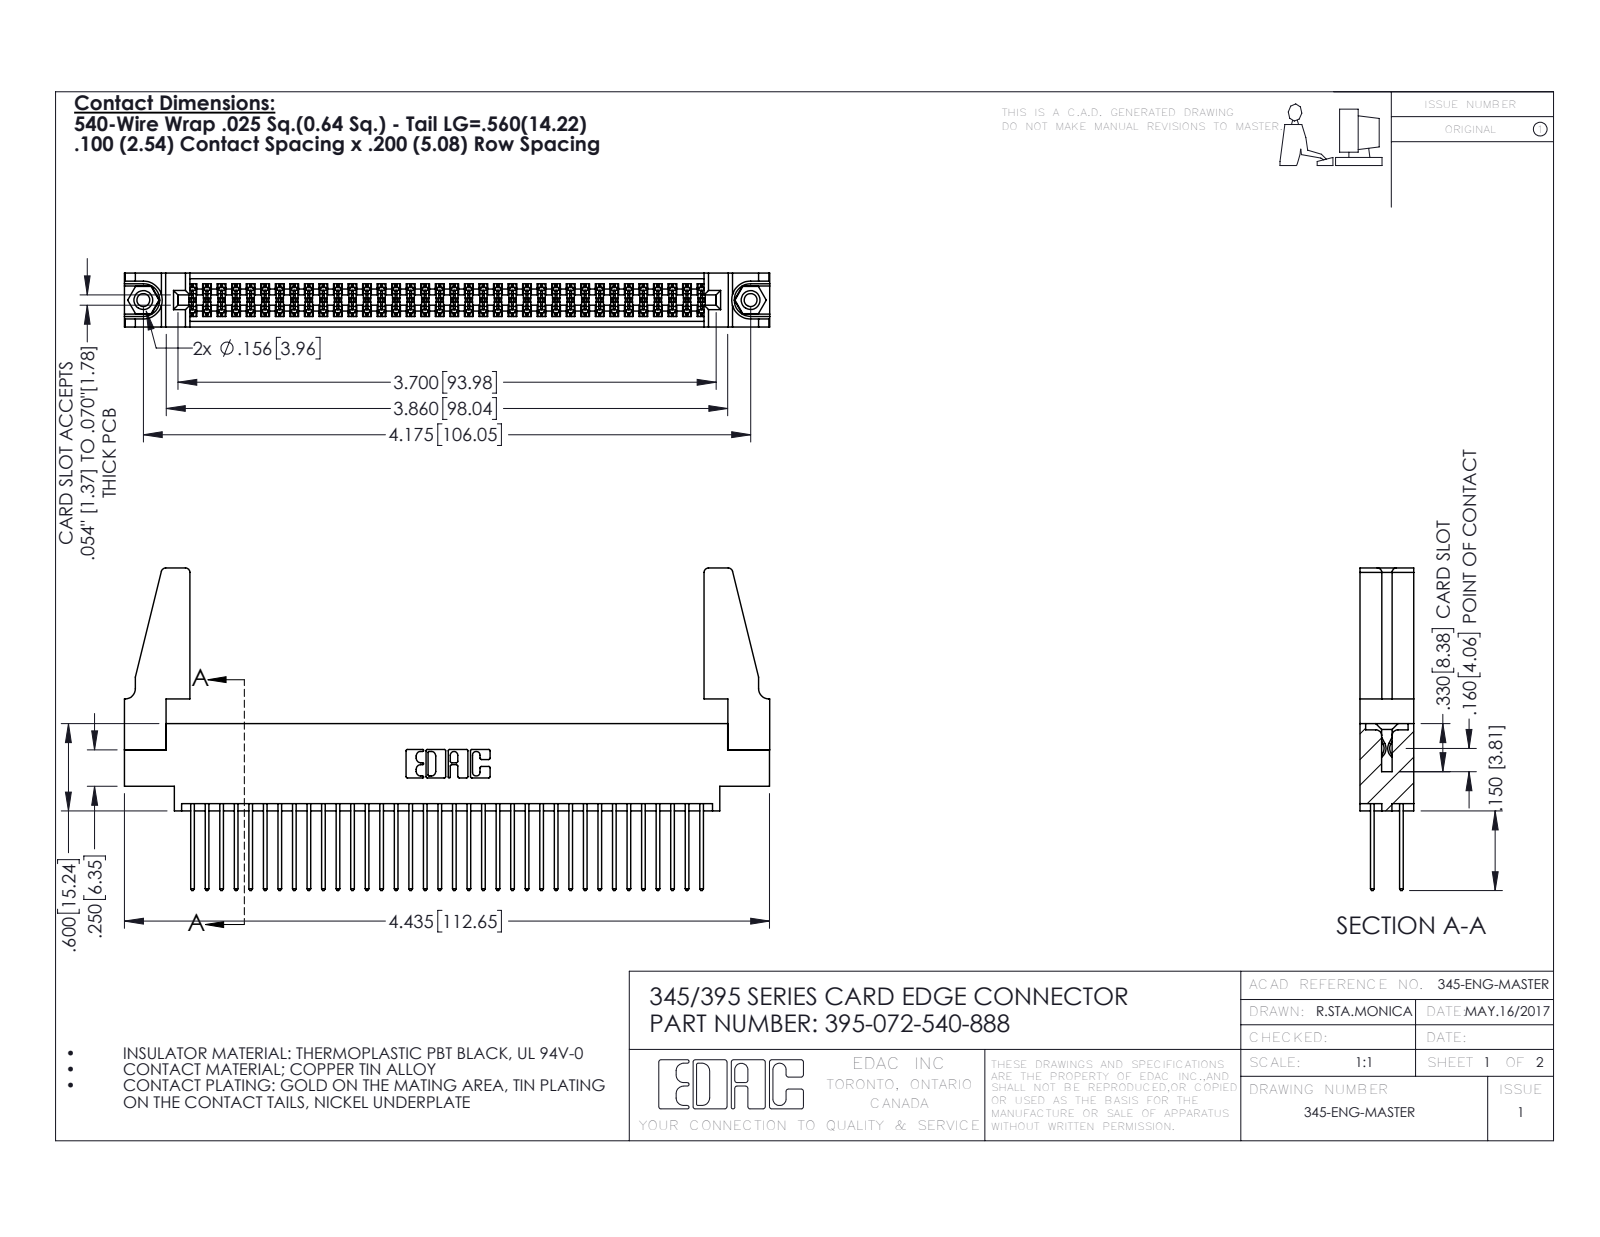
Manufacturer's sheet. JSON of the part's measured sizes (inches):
{"part_name": "345-292-001_345-293-140; 345 Part_0.170 Offset - 0.156 Dia-TH; 345-250-001_345-250-001-102; 395-072-540-888 (+1 more)", "step_written_by": "SolidWorks 2016 (CONFIG_CONTROL_DESIGN)", "units": "inches", "bodies": {"solids": 77, "faces": 3854, "planar": 2532, "cylindrical": 1306, "other": 16}, "overall_size": [4.436, 2.217, 0.37], "volume_in3": 0.873, "surface_area_in2": 32.16, "round_holes": [[0.089, 2], [0.125, 2], [0.156, 2], [0.064, 1]], "round_bosses_or_shafts": [[0.155, 2]], "partial_cylinders_radius": [[0.006, 108], [0.01, 72], [0.01, 22], [0.03, 8], [0.007, 6], [0.031, 6], [0.026, 3], [0.014, 2]], "face_to_face_distances": [0.072, 0.298, 0.37, 0.2, 0.098, 0.272, 0.025, 0.225, 0.175, 0.149], "hole_center_spacings": [0.27, 3.939, 4.175]}
